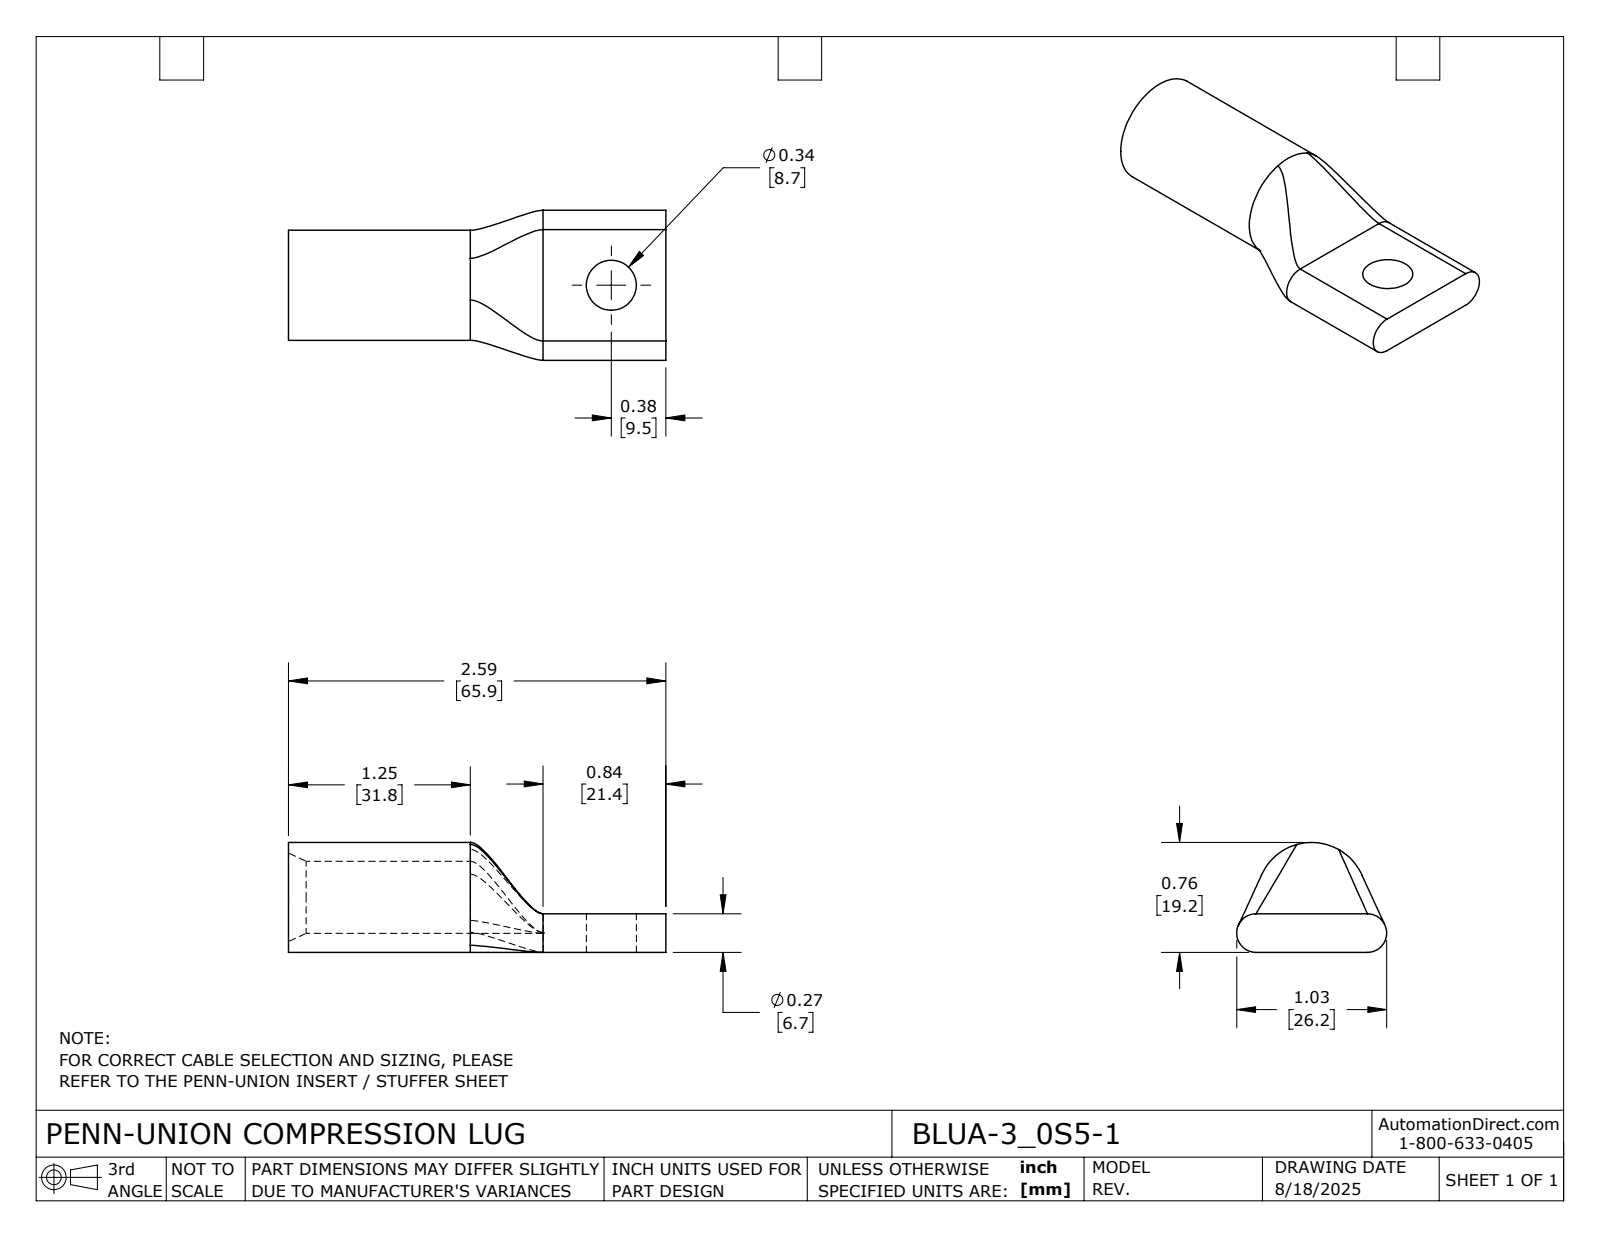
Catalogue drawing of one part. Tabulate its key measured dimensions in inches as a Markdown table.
| quantity | value |
| --- | --- |
| part name | BLUA-3_0S5-1 |
| STEP written by | SolidWorks 2024 (CONFIG_CONTROL_DESIGN) |
| units | inches |
| bodies | 1 solid, 24 faces (5 planar, 9 cylindrical, 10 other) |
| overall size | 2.594 × 1.031 × 0.756 |
| volume | 0.636 in³ |
| surface area | 9.676 in² |
| round holes (diameter × count) | 0.344 × 1, 0.495 × 1 |
| round bosses / shafts (diameter × count) | 0.756 × 1 |
| partial cylindrical surfaces (radius × count) | 0.133 × 2 |
| main face-to-face distances | 0.266, 2.594, 1.75, 0.844 |
